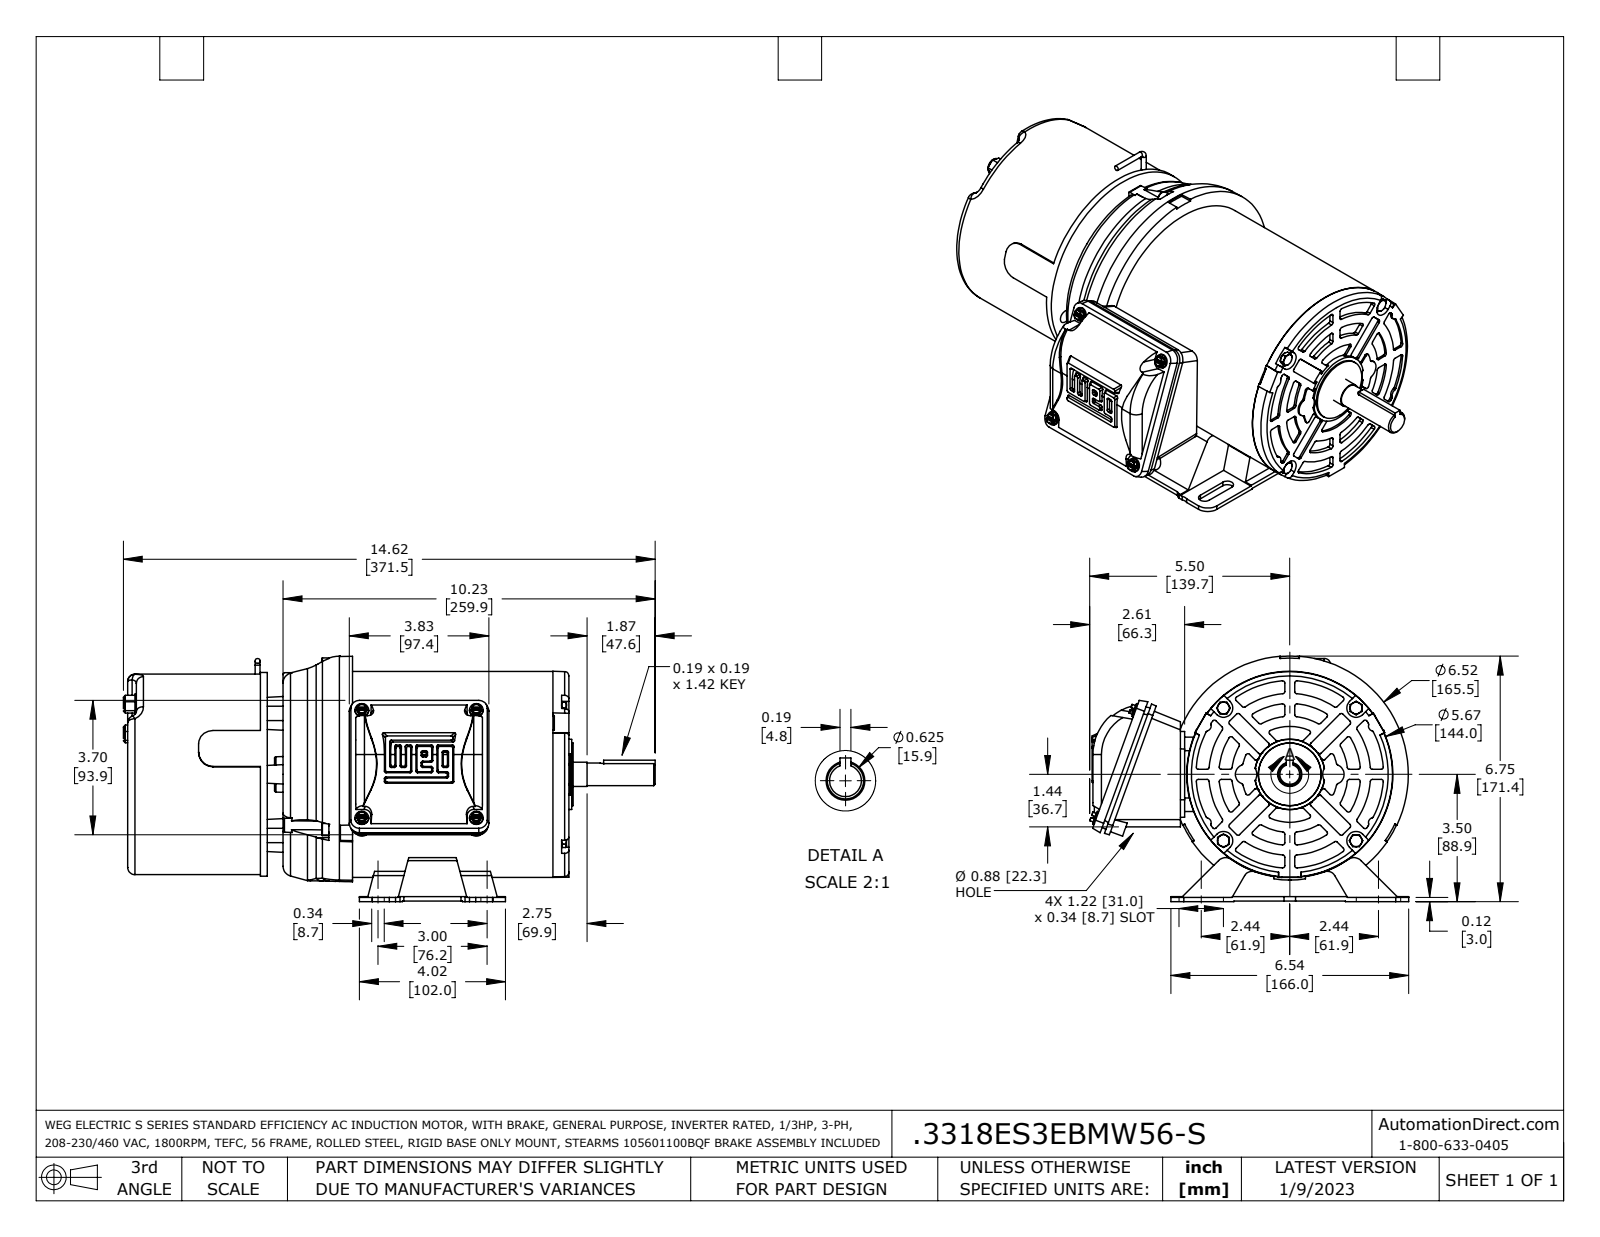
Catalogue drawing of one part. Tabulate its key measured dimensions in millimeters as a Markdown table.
| quantity | value |
| --- | --- |
| part name | W56_3PH_TEFC_BM_1461 coord fxt |
| STEP written by | SolidWorks 2021 (AUTOMOTIVE_DESIGN) |
| units | millimeters |
| bodies | 16 solids, 1499 faces (582 planar, 422 cylindrical, 495 other) |
| overall size | 371.4 × 222.7 × 171.5 |
| volume | 5 006 000 mm³ |
| surface area | 443 900 mm² |
| round holes (diameter × count) | 6 × 4, 6.4 × 2, 7.1 × 2, 9.4 × 2, 12.7 × 1, 76.2 × 1, 131 × 1 |
| round bosses / shafts (diameter × count) | 9.5 × 4, 4.7 × 4, 8.5 × 3, 5 × 3, 14 × 2, 11.1 × 2, 3.5 × 2, 143.7 × 1 |
| partial cylindrical surfaces (radius × count) | 1.5 × 92, 1.2 × 38, 5 × 15, 0.5 × 10, 4.3 × 8, 5.2 × 8, 7 × 8, 3.5 × 4 |
| main face-to-face distances | 140, 14.5, 154.5, 45, 181, 26.5, 41, 18.5, 59.5, 199.5 |
| hole center spacings | 80, 18.2, 47.6, 56.6, 59.4, 80, 106.1, 113.1 |
